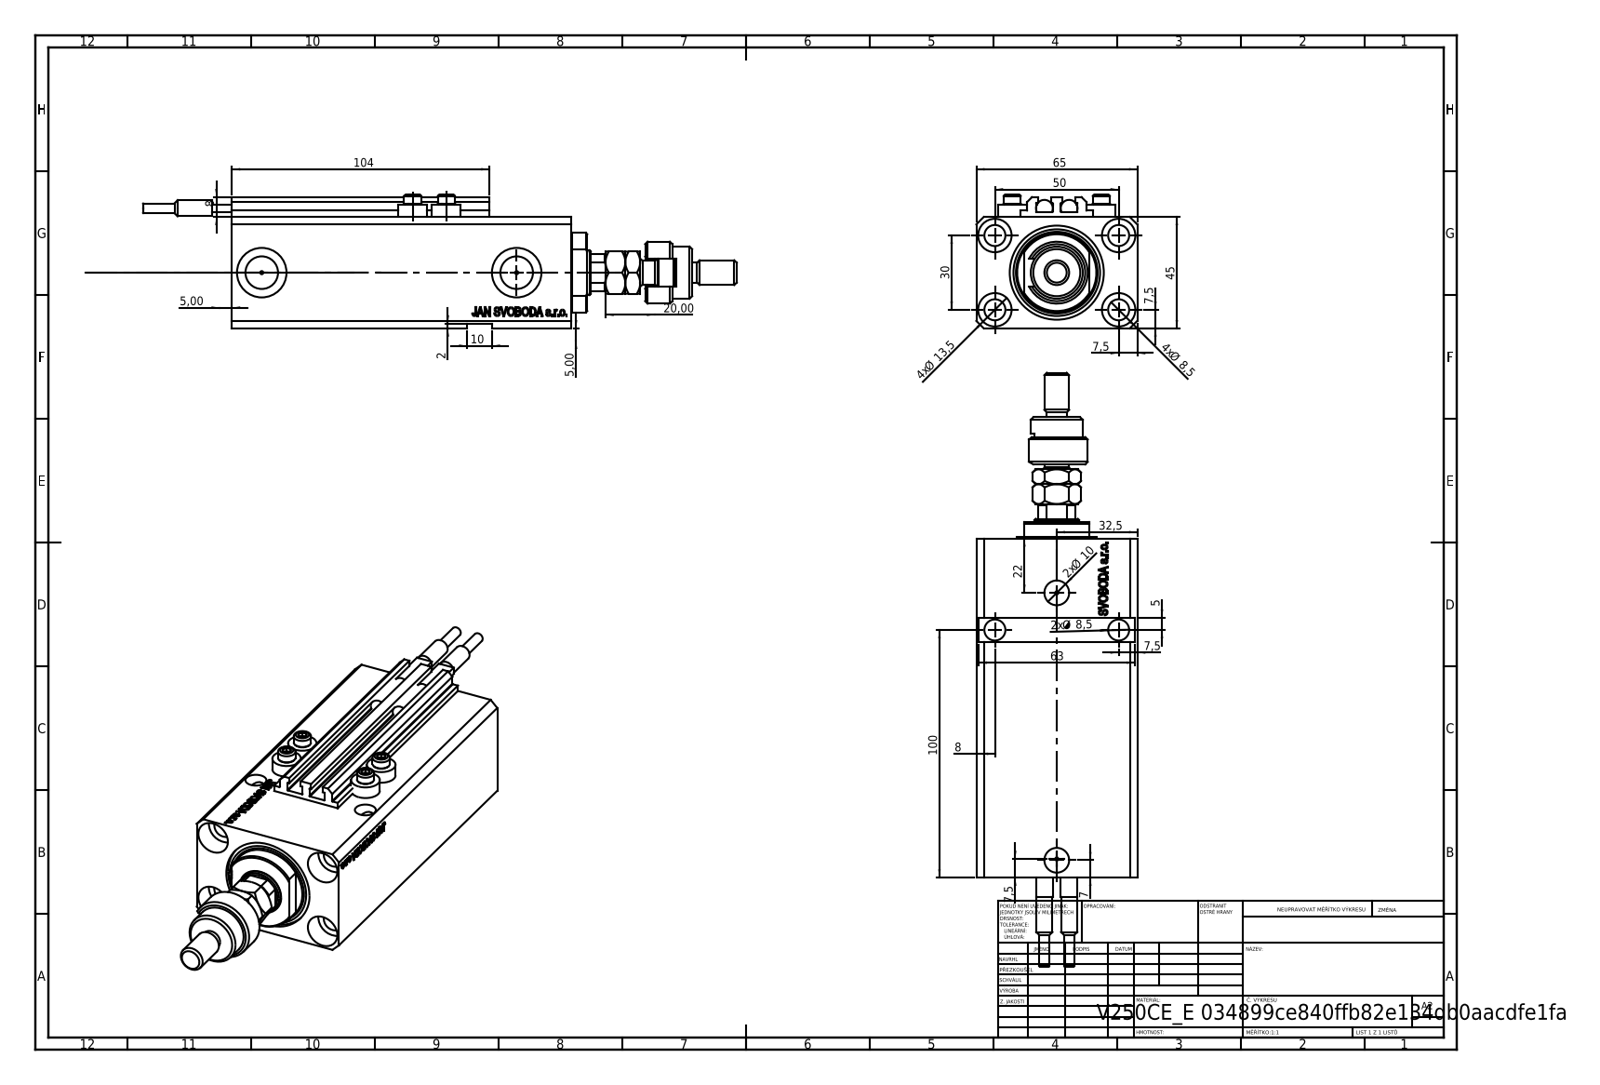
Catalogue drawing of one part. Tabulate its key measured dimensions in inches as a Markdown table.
| quantity | value |
| --- | --- |
| part name | FEMALE_PART_FOR_DFA; ALLEN BOLT V250CE; V250CE_VC_E; V250CE_E_Body (+3 more) |
| STEP written by | SolidWorks 2019 (CONFIG_CONTROL_DESIGN) |
| units | inches |
| bodies | 12 solids, 1204 faces (571 planar, 151 cylindrical, 482 other) |
| overall size | 9.445 × 2.559 × 2.126 |
| volume | 22.54 in³ |
| surface area | 159.4 in² |
| round holes (diameter × count) | 0.335 × 7, 0.049 × 4, 0.157 × 4, 0.531 × 4, 0.394 × 2, 0.518 × 2, 0.787 × 2, 0.709 × 1, 1.496 × 1 |
| round bosses / shafts (diameter × count) | 0.457 × 4, 0.276 × 4, 0.268 × 2, 0.256 × 2, 0.157 × 2, 0.984 × 1, 0.827 × 1, 0.63 × 1 |
| partial cylindrical surfaces (radius × count) | 0.008 × 10, 0.217 × 1, 0.335 × 1, 0.344 × 1, 0.63 × 1 |
| main face-to-face distances | 1.772, 2.559, 0.079, 1.85, 0.118, 0.098, 4.406, 0.394, 0.988, 5.394 |
| hole center spacings | 1.148, 1.969, 0.535, 0.595, 1.098, 1.181, 1.324, 1.417 |
